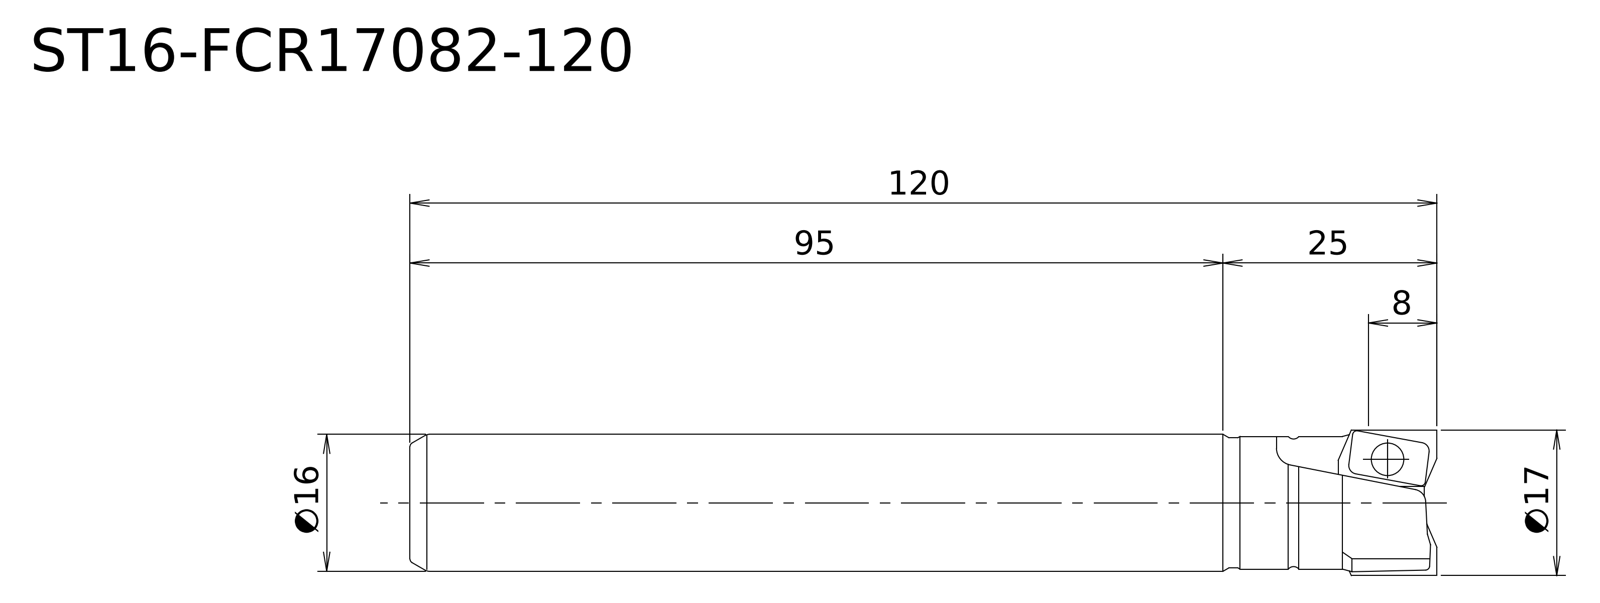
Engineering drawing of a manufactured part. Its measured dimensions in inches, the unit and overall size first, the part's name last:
Units: inches
Overall size (bounding box): 4.724 × 0.669 × 0.669
Round bosses / shafts (diameter × count): ⌀0.669 ×1, ⌀0.63 ×1, ⌀0.61 ×1
Main face-to-face distances: 4.724
Volume: 1.478 in³ · Surface area: 10.06 in²
Bodies: 1 solid, 8 faces (2 planar, 3 cylindrical, 3 other)
STEP written by: Kubotek KeyCreator V8.5.1 (14335) (CONFIG_CONTROL_DESIGN)
